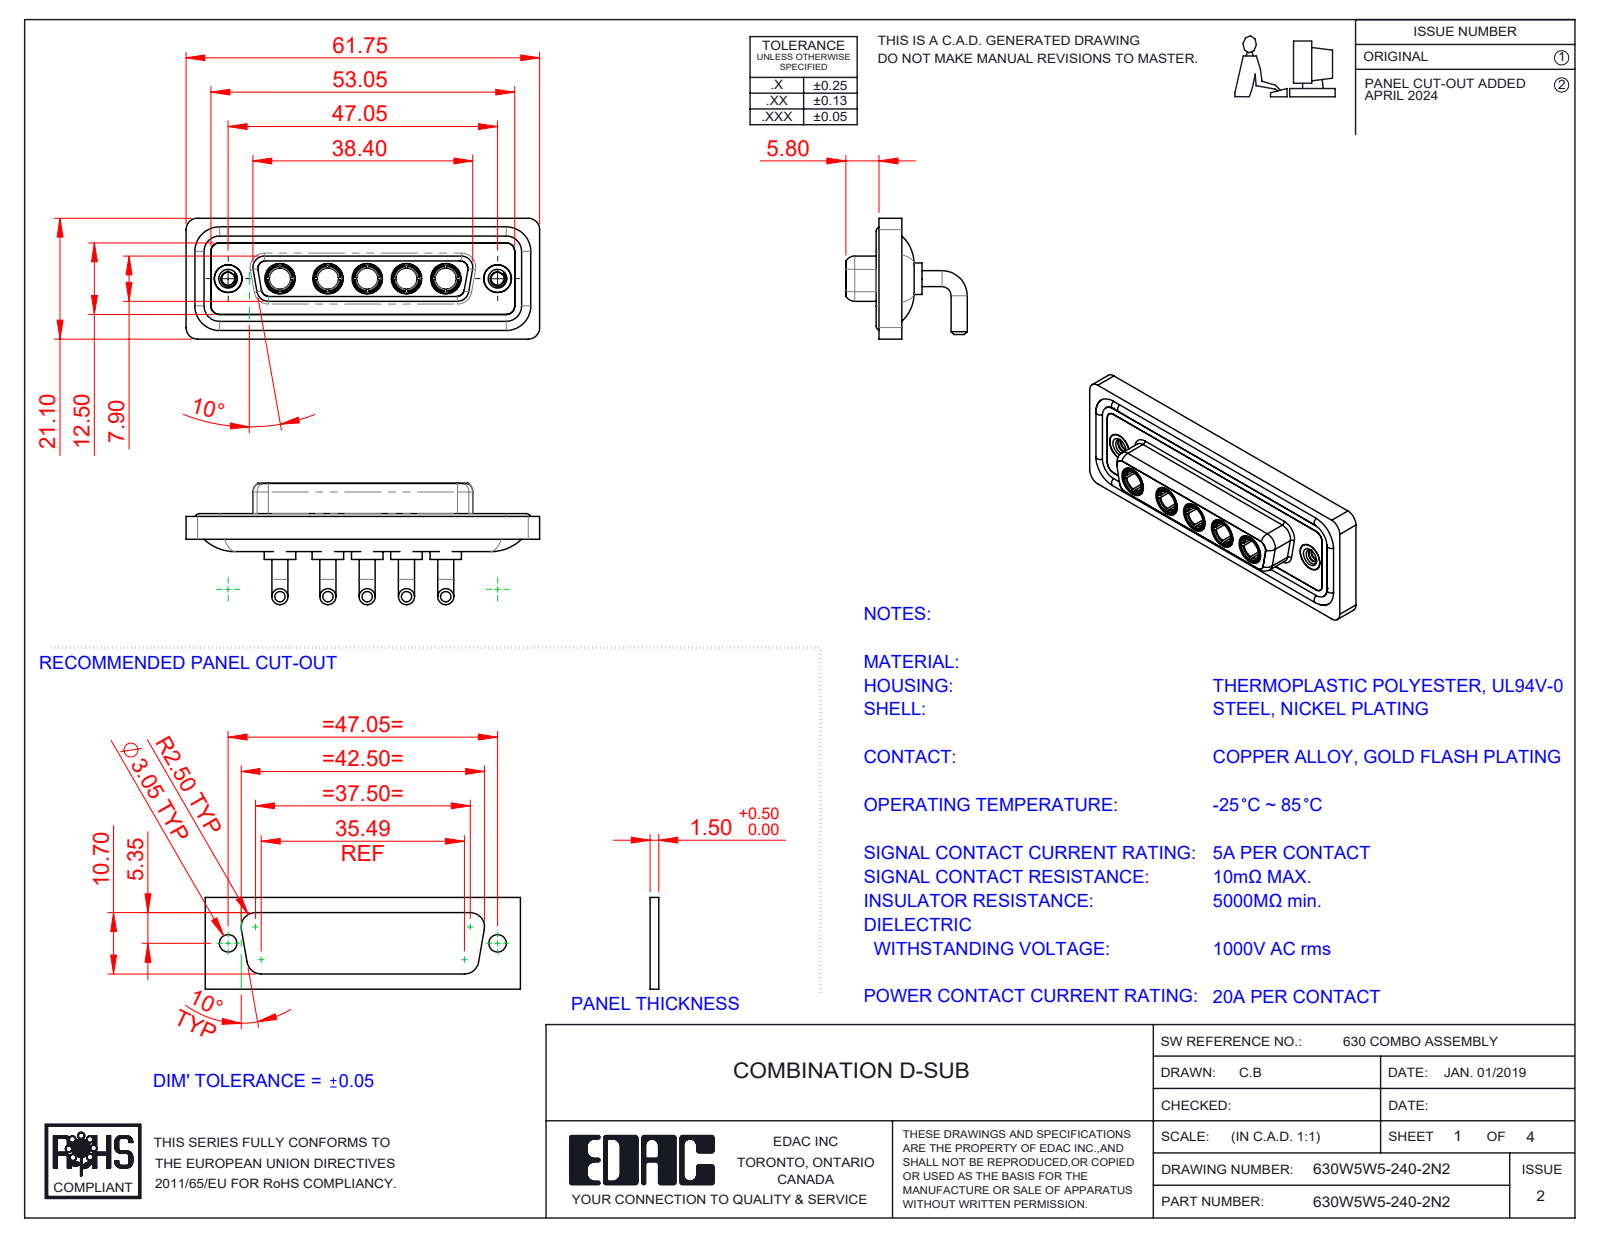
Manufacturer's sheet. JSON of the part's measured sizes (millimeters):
{"part_name": "630Combo Threaded Rivet_2; Power Socket_20A RA; 630Combo Shell Rear_25 Contacts; 630W5W5-240-2N2 (+3 more)", "step_written_by": "SolidWorks 2023 (CONFIG_CONTROL_DESIGN)", "units": "millimeters", "bodies": {"solids": 17, "faces": 776, "planar": 250, "cylindrical": 313, "other": 213}, "overall_size": [61.75, 21.2, 21.1], "volume_mm3": 8435, "surface_area_mm2": 13813, "round_holes": [[4.85, 7], [3.7, 5], [5.3, 5], [2.26, 2], [4, 2], [4.05, 2], [5, 2]], "round_bosses_or_shafts": [[2.8, 10], [5.5, 5], [5.2, 5], [4.96, 5], [4.75, 5], [3.75, 5], [1.6, 4], [4.95, 2]], "partial_cylinders_radius": [[1.5, 18], [2, 18], [1.35, 8], [1.6, 8], [2.1, 5], [0.25, 4], [0.5, 4], [0.6, 4]], "face_to_face_distances": [0.4, 1.8, 4.1, 1.1, 1.5, 2.5, 3.1, 3.7, 1.6, 2.9], "hole_center_spacings": [6.86, 9.04, 38.01, 6.87, 8.38, 13.72, 13.73, 15.25]}
